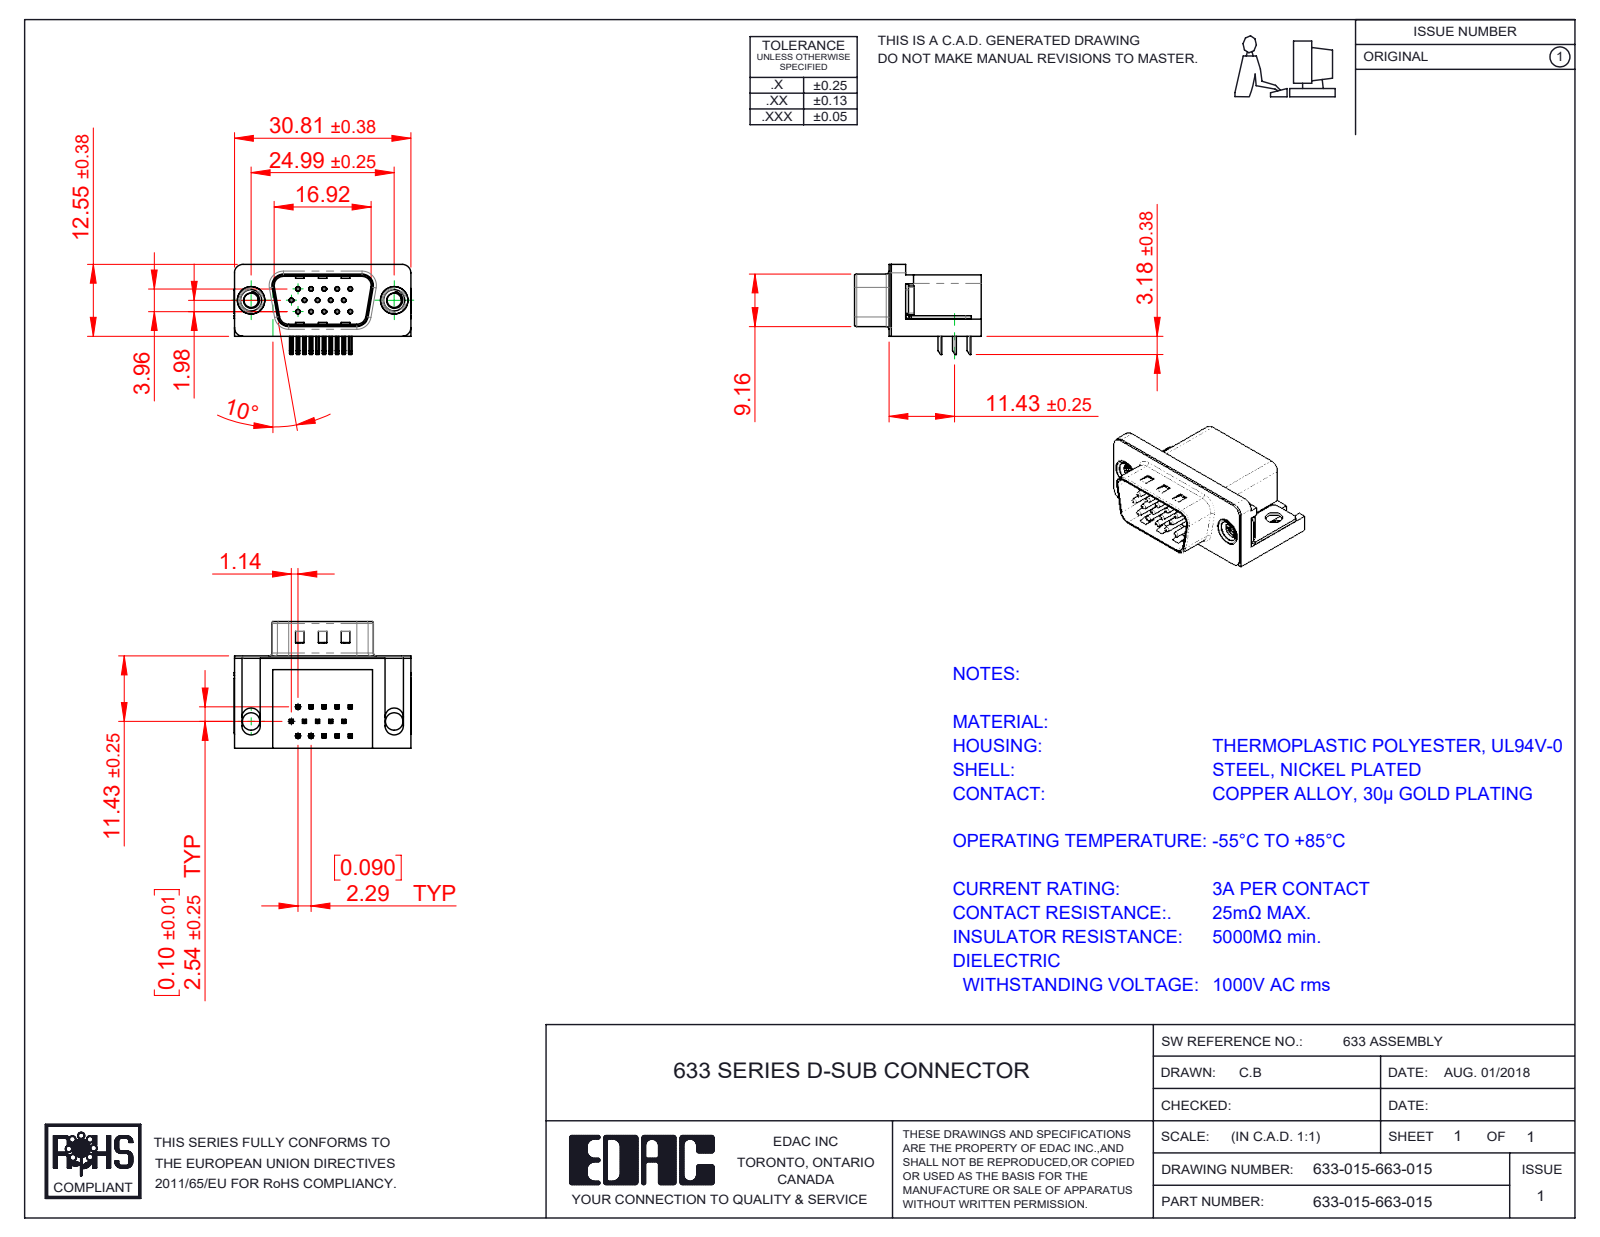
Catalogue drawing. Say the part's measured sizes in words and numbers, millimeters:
The part is named "633 Contact Middle; 633 Thru Hole Board Mount; 633 M3 Threaded Rivet; 633 Contact Bottom (+4 more)". Its 3-D file was written by "SolidWorks 2016 (CONFIG_CONTROL_DESIGN)". It is 21 solids with 1441 faces: 859 planar, 447 cylindrical and 135 other. Overall it measures 30.89 by 22.1 by 15.73 millimeters. Its volume is 4 066 cubic millimeters and its surface area 5 416 square millimeters. Round holes: 15 of diameter 0.35, 15 of diameter 0.8, 2 of diameter 2.5, 2 of diameter 3.05, 2 of diameter 4, 2 of diameter 4.8, 2 of diameter 5. Round bosses or shafts: 15 of diameter 0.75, 2 of diameter 4.9, 2 of diameter 4.75, 2 of diameter 3.9. Partial cylindrical surfaces (rounded edges, fillets, slot ends): 68 of radius 0.25, 30 of radius 0.12, 16 of radius 1, 9 of radius 0.5, 8 of radius 1.6, 7 of radius 1.5, 4 of radius 0.9, 4 of radius 2. The main face-to-face distances are 0.4, 10.35, 15.7, 2.9, 0.5, 6.7, 16.1, 2.5, 0.35, 10.7. The hole center spacings are 3.96, 2.28, 4.57, 2.29, 6.05, 6.86, 7.92, 6.04.
